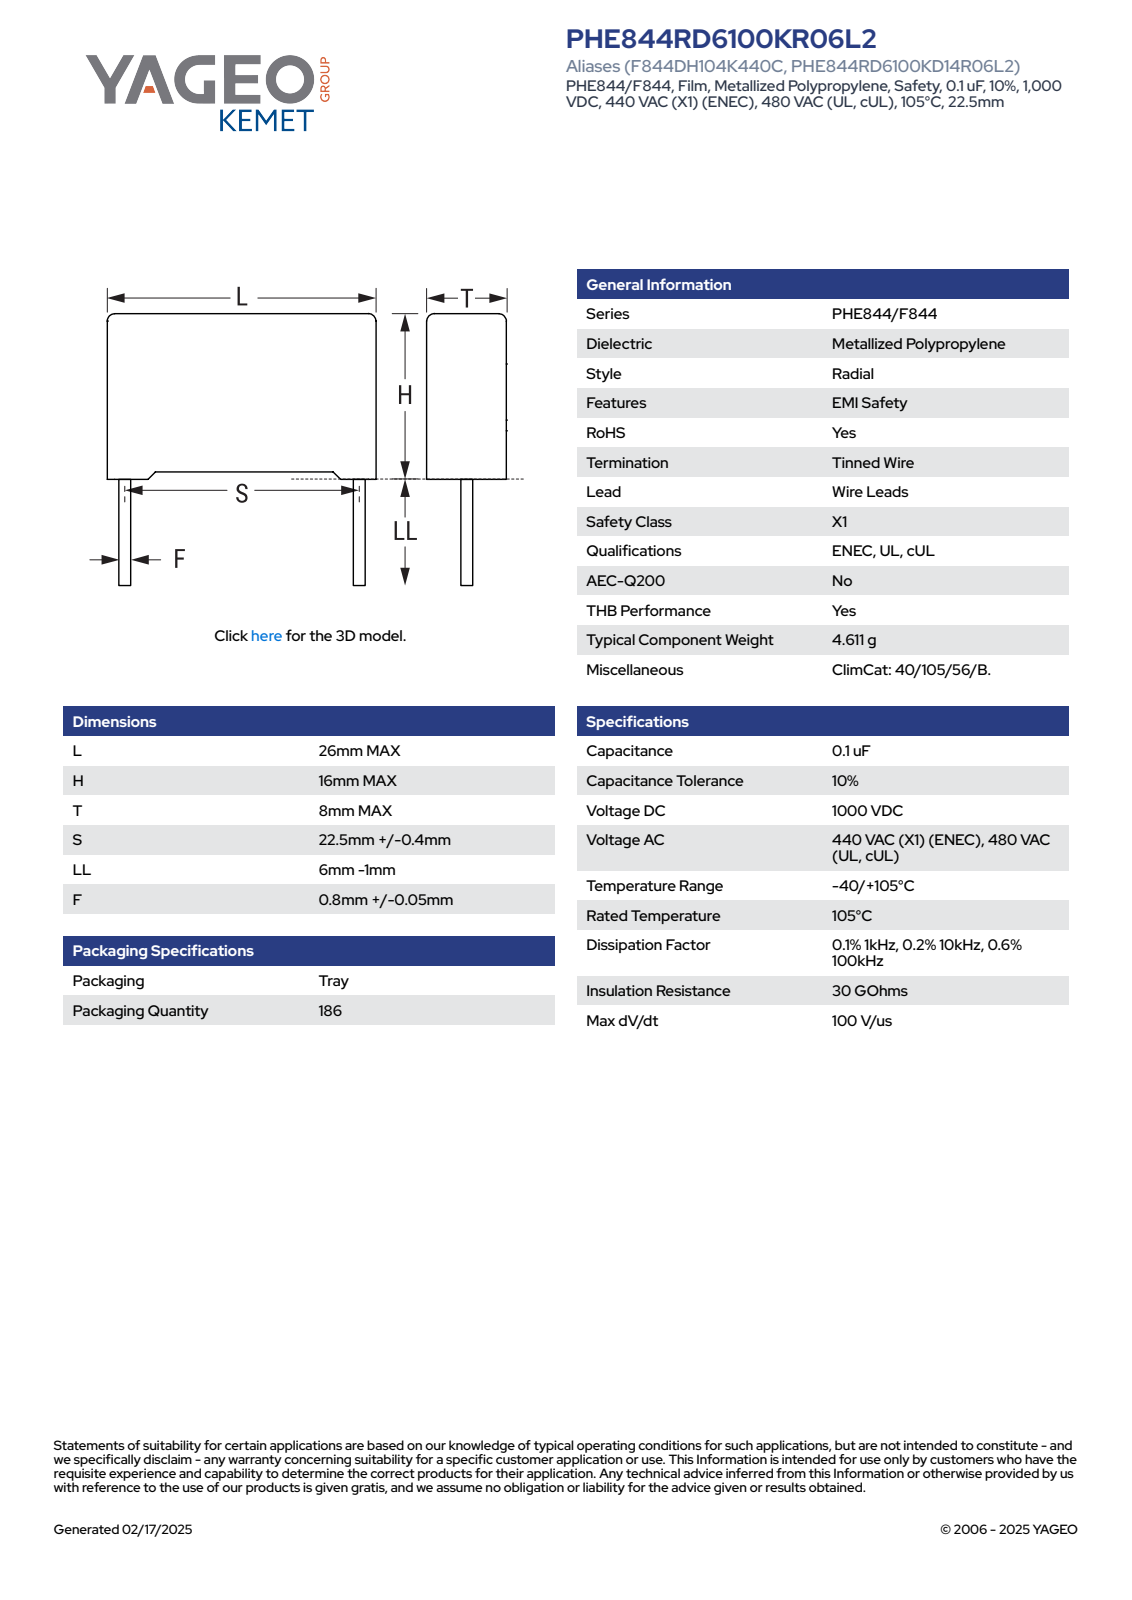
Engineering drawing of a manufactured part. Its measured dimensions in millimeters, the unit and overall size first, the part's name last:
Units: millimetres
Overall size (bounding box): 26 × 21 × 8.01
Round bosses / shafts (diameter × count): ⌀0.85 ×2
Partial cylindrical surfaces — rounded edges, fillets, slot ends (radius × count): R0.5 ×4
Main face-to-face distances: 8, 15.25, 26, 15.45, 0.87, 0.55, 0.75, 16, 7.13, 8.01
Volume: 3 199 mm³ · Surface area: 1 576 mm²
Bodies: 4 solids, 85 faces (77 planar, 8 cylindrical, 0 other)
Part name (STEP PRODUCT): CFR_RB2_26X16X8_L26H16T8S22.5LL5F0.85
STEP written by: SolidWorks 2021 (AUTOMOTIVE_DESIGN)
